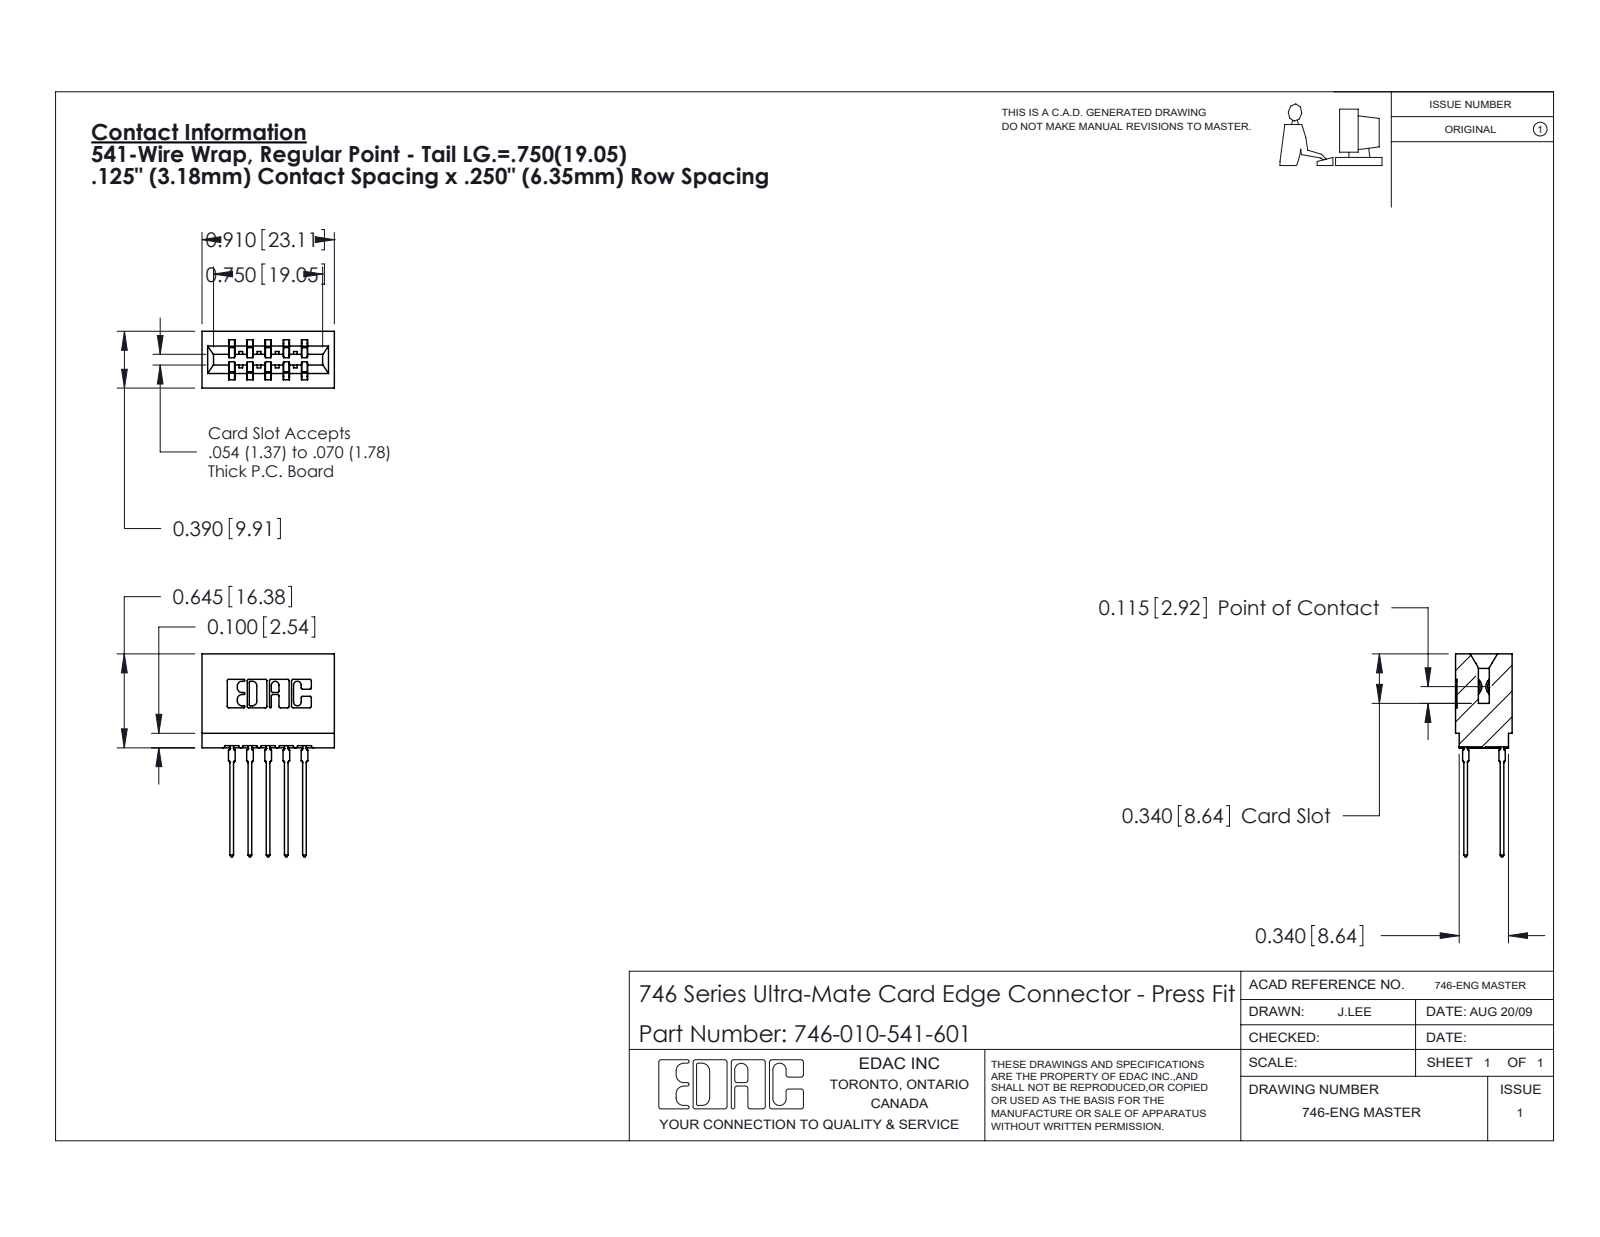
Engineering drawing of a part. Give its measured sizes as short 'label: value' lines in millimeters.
name: 746-010-541-601; 746-292-001_541; 746 Part_.340 Slot Depth - 01
written by: SolidWorks 2020 (CONFIG_CONTROL_DESIGN)
unit: mm
bodies: 11 solids, 992 faces (515 planar, 217 cylindrical, 260 other)
size: 35.4 × 23.1 × 9.9
volume: 2 920 mm³; area: 3 872 mm²
rounds: 22× R0.3, 20× R0.5, 8× R0.1, 8× R0.3, 6× R0.2, 6× R0.4, 6× R0.8, 3× R0.7
face distances: 6.4, 1.4, 8.5, 1.1, 3.2, 3.2, 2.1, 0.6, 7.8, 9.9
